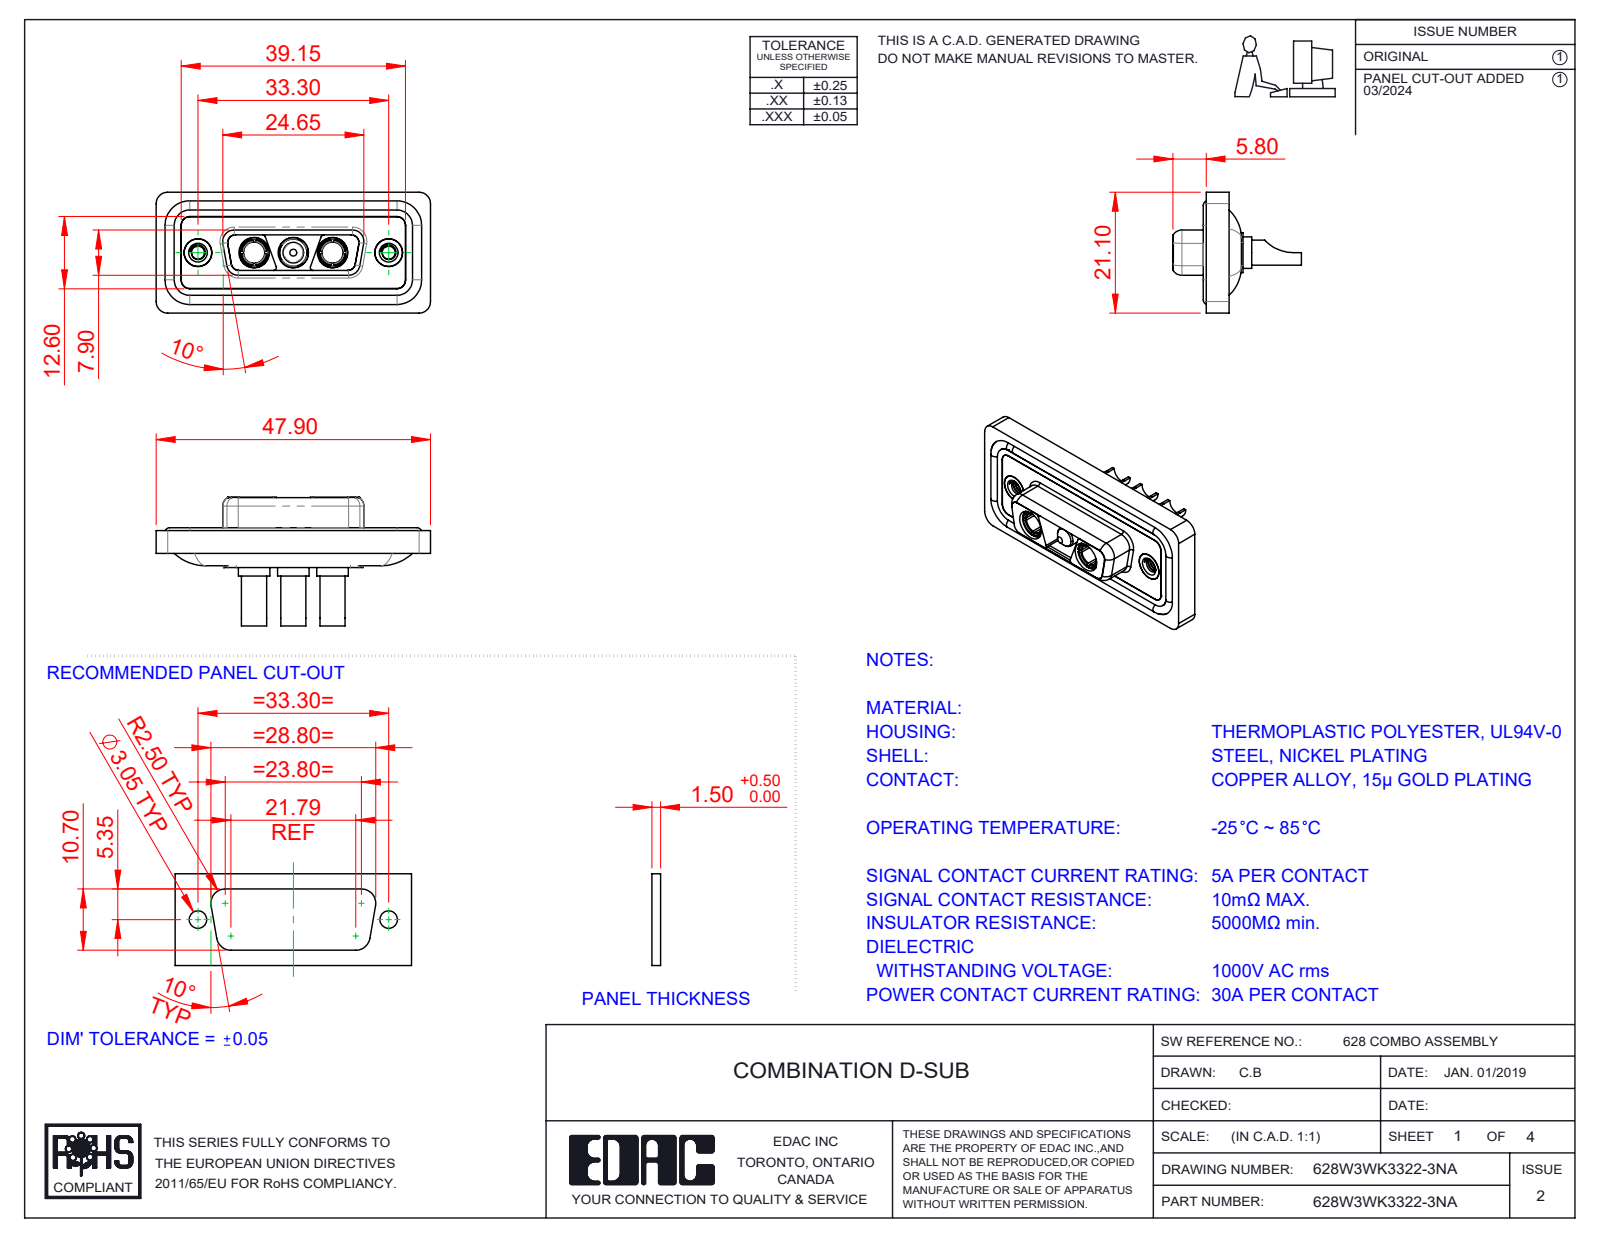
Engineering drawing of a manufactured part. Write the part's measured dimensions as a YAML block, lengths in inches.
part_name: "628Combo Waterproof Housing_15 Contacts; 628Combo Shell Front_15 Contacts; Power Socket_30A SC; 628Combo Shell Rear_15 Contacts (+4 more)"
step_written_by: "SolidWorks 2023 (CONFIG_CONTROL_DESIGN)"
units: inches
bodies: {solids: 13, faces: 599, planar: 187, cylindrical: 269, other: 143}
overall_size: [1.886, 0.884, 0.831]
volume: 0.363
surface_area: 15.23
round_holes:
  - {diameter: 0.191, count: 5}
  - {diameter: 0.138, count: 3}
  - {diameter: 0.209, count: 3}
  - {diameter: 0.089, count: 2}
  - {diameter: 0.146, count: 2}
  - {diameter: 0.157, count: 2}
  - {diameter: 0.159, count: 2}
  - {diameter: 0.197, count: 2}
round_bosses_or_shafts:
  - {diameter: 0.063, count: 4}
  - {diameter: 0.217, count: 3}
  - {diameter: 0.205, count: 3}
  - {diameter: 0.187, count: 3}
  - {diameter: 0.173, count: 3}
  - {diameter: 0.148, count: 3}
  - {diameter: 0.195, count: 2}
  - {diameter: 0.195, count: 2}
partial_cylinders:
  - {radius: 0.059, count: 22}
  - {radius: 0.079, count: 20}
  - {radius: 0.053, count: 12}
  - {radius: 0.02, count: 8}
  - {radius: 0.063, count: 8}
  - {radius: 0.01, count: 4}
  - {radius: 0.024, count: 4}
  - {radius: 0.026, count: 4}
face_to_face_distances: [0.016, 0.063, 0.02, 0.043, 0.114, 0.071, 0.222, 0.278, 0.211, 0.26]
hole_center_spacings: [0.27, 0.386, 0.656, 0.925, 0.539, 1.311]
